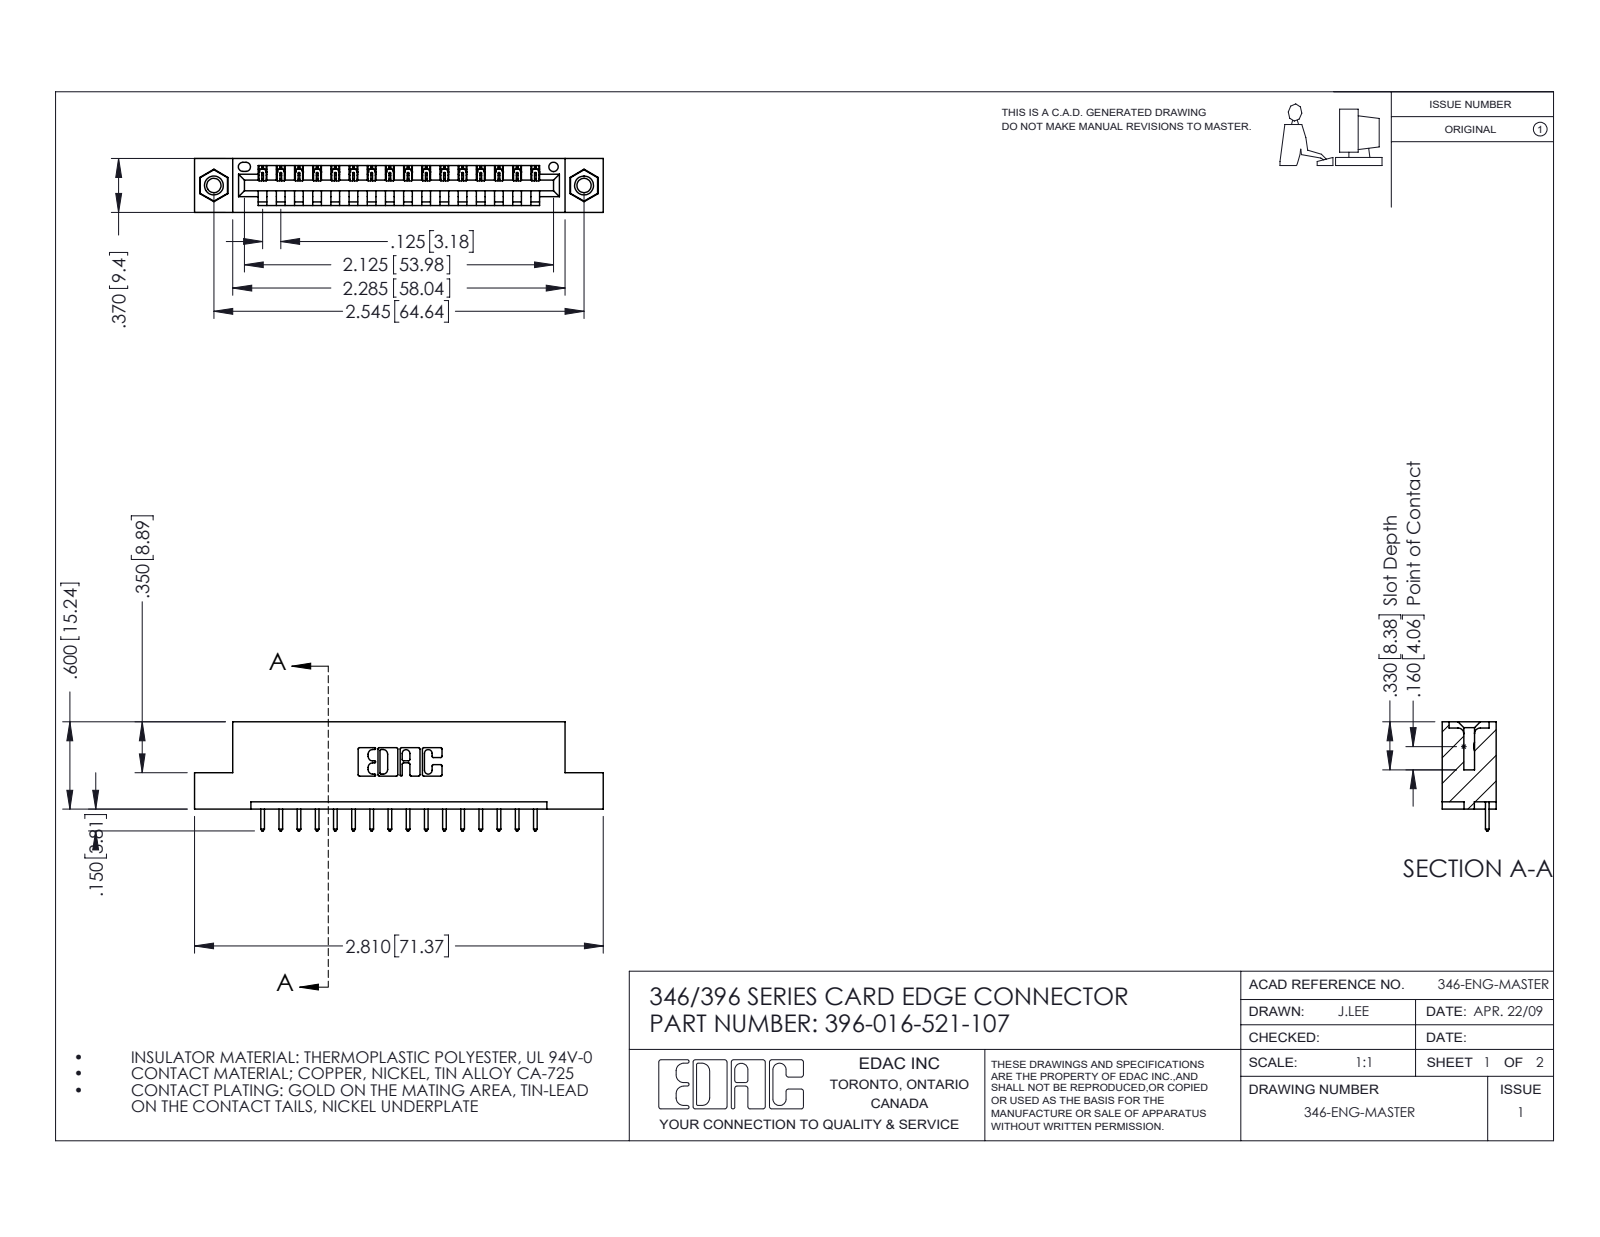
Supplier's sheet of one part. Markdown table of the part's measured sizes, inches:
| quantity | value |
| --- | --- |
| part name | 346 Part_Flush Mounting Lugs - 0.156 Dia-TI; 396-016-521-107; 345-250-001_345-250-005-103; 345-292-001_345-293-121 |
| STEP written by | SolidWorks 2016 (CONFIG_CONTROL_DESIGN) |
| units | inches |
| bodies | 19 solids, 1110 faces (748 planar, 346 cylindrical, 16 other) |
| overall size | 2.81 × 0.75 × 0.37 |
| volume | 0.402 in³ |
| surface area | 12.11 in² |
| round holes (diameter × count) | 0.098 × 2, 0.125 × 2, 0.156 × 2, 0.064 × 1 |
| round bosses / shafts (diameter × count) | 0.155 × 2 |
| partial cylindrical surfaces (radius × count) | 0.006 × 32, 0.01 × 32, 0.01 × 22, 0.007 × 6, 0.031 × 6, 0.026 × 3, 0.031 × 2, 0.04 × 2 |
| main face-to-face distances | 0.048, 0.322, 0.25, 0.37, 0.072, 0.298, 0.025, 0.148, 0.222, 0.1 |
| hole center spacings | 0.246, 2.338, 2.545 |
